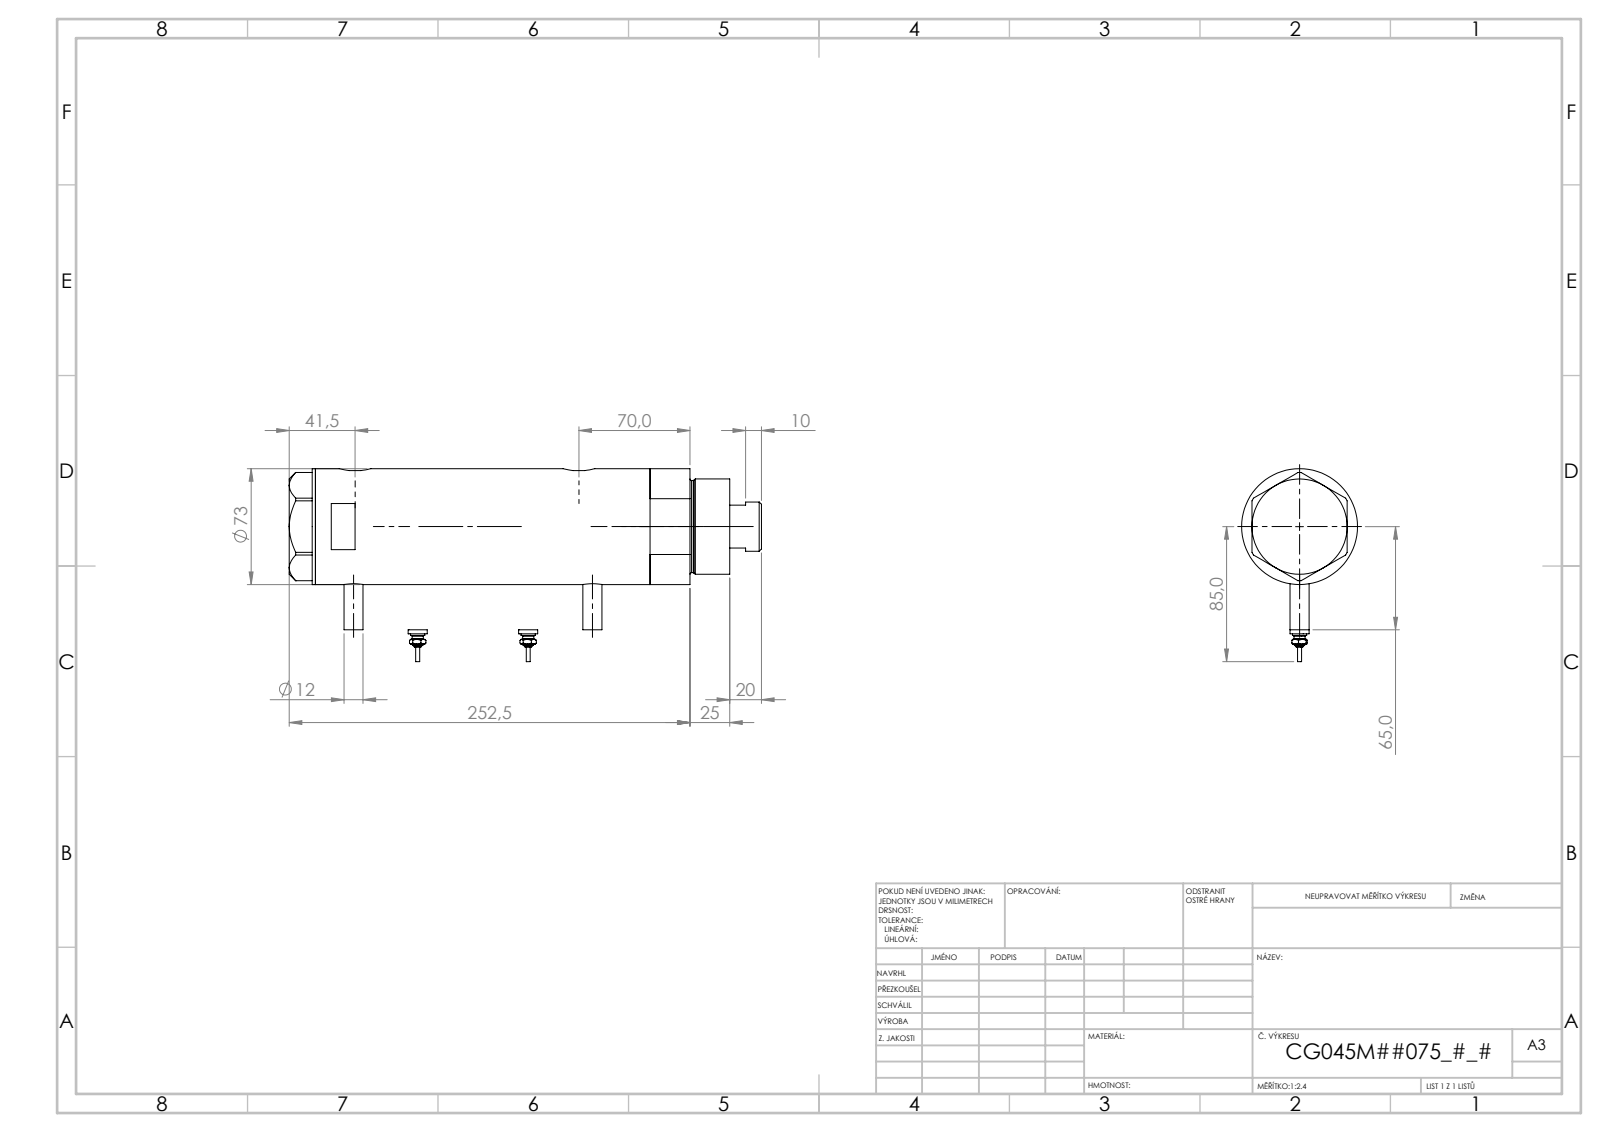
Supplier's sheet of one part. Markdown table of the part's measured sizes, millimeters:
| quantity | value |
| --- | --- |
| part name | V270CG_VC; V270CG_SWITCH; V270CG_FRONT; V270CG_MIDDLE (+1 more) |
| STEP written by | SolidWorks 2019 (CONFIG_CONTROL_DESIGN) |
| units | millimeters |
| bodies | 6 solids, 231 faces (78 planar, 79 cylindrical, 74 other) |
| overall size | 266.52 × 105.3 × 73 |
| volume | 924 552 mm³ |
| surface area | 157 230 mm² |
| round holes (diameter × count) | 5 × 2, 12.5 × 2, 13.16 × 2, 10.5 × 1, 32 × 1, 33.5 × 1, 45 × 1, 48 × 1, 64 × 1 |
| round bosses / shafts (diameter × count) | 12 × 3, 9 × 2, 7 × 2, 4.34 × 2, 2.4 × 2, 73 × 1, 60 × 1, 58 × 1 |
| partial cylindrical surfaces (radius × count) | 10 × 2 |
| main face-to-face distances | 142.14, 26, 116.14, 16.5, 42.5, 158.64, 230.01, 246.51, 204.01, 87.87 |
| hole center spacings | 126.65, 0.99, 1, 8.5, 8.51, 117.15, 118.14, 118.15 |
